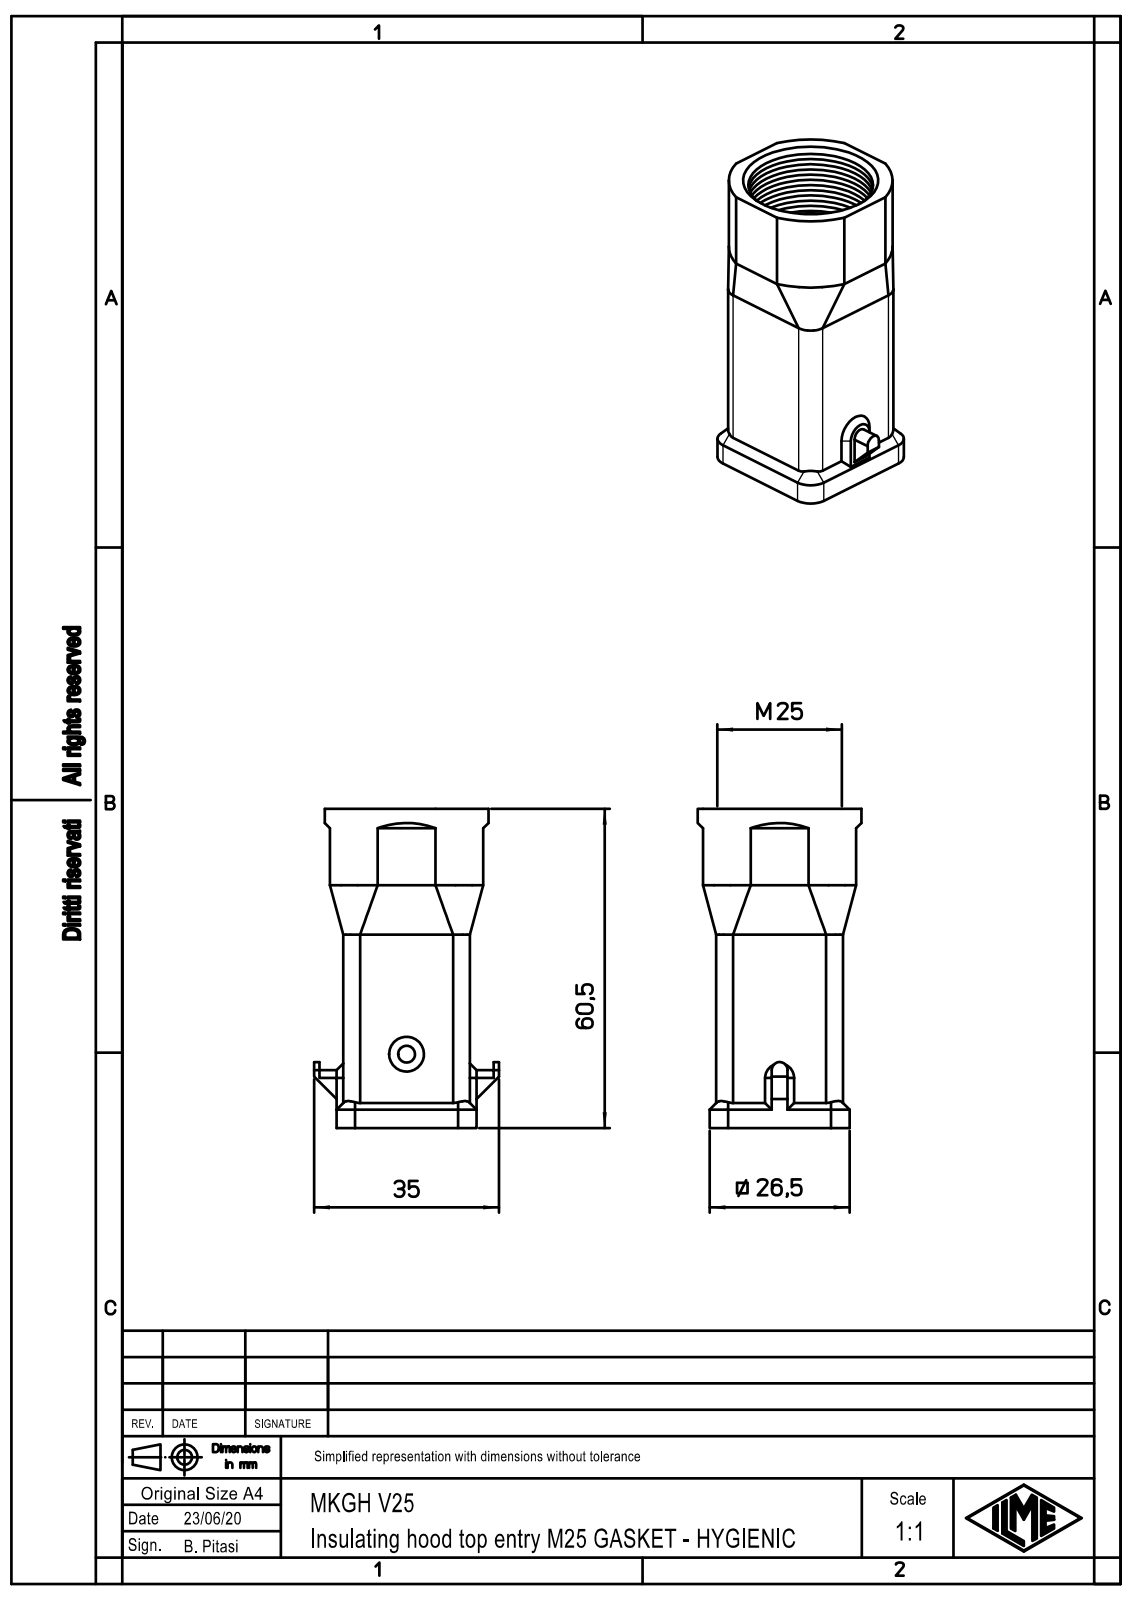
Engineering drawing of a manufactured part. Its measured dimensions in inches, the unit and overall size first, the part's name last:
Units: inches
Overall size (bounding box): 2.382 × 1.378 × 1.22
Round holes (diameter × count): ⌀0.126 ×1
Round bosses / shafts (diameter × count): ⌀1.22 ×1
Partial cylindrical surfaces — rounded edges, fillets, slot ends (radius × count): R0.079 ×8, R0.075 ×4, R0.126 ×4, R0.138 ×4, R0.059 ×2
Main face-to-face distances: 0.945, 1.043, 0.049, 0.098, 1.093, 0.994, 1.142, 0.15, 0.992, 0.1
Volume: 0.698 in³ · Surface area: 17.66 in²
Bodies: 1 solid, 112 faces (67 planar, 28 cylindrical, 17 other)
Part name (STEP PRODUCT): MKGH V25; MKGH V25.stp
STEP written by: Creo Elements/Direct Modeling 20.1B 02-Apr-2019 (C) Parametric Technology GmbH (AUTOMOTIVE_DESIGN)
